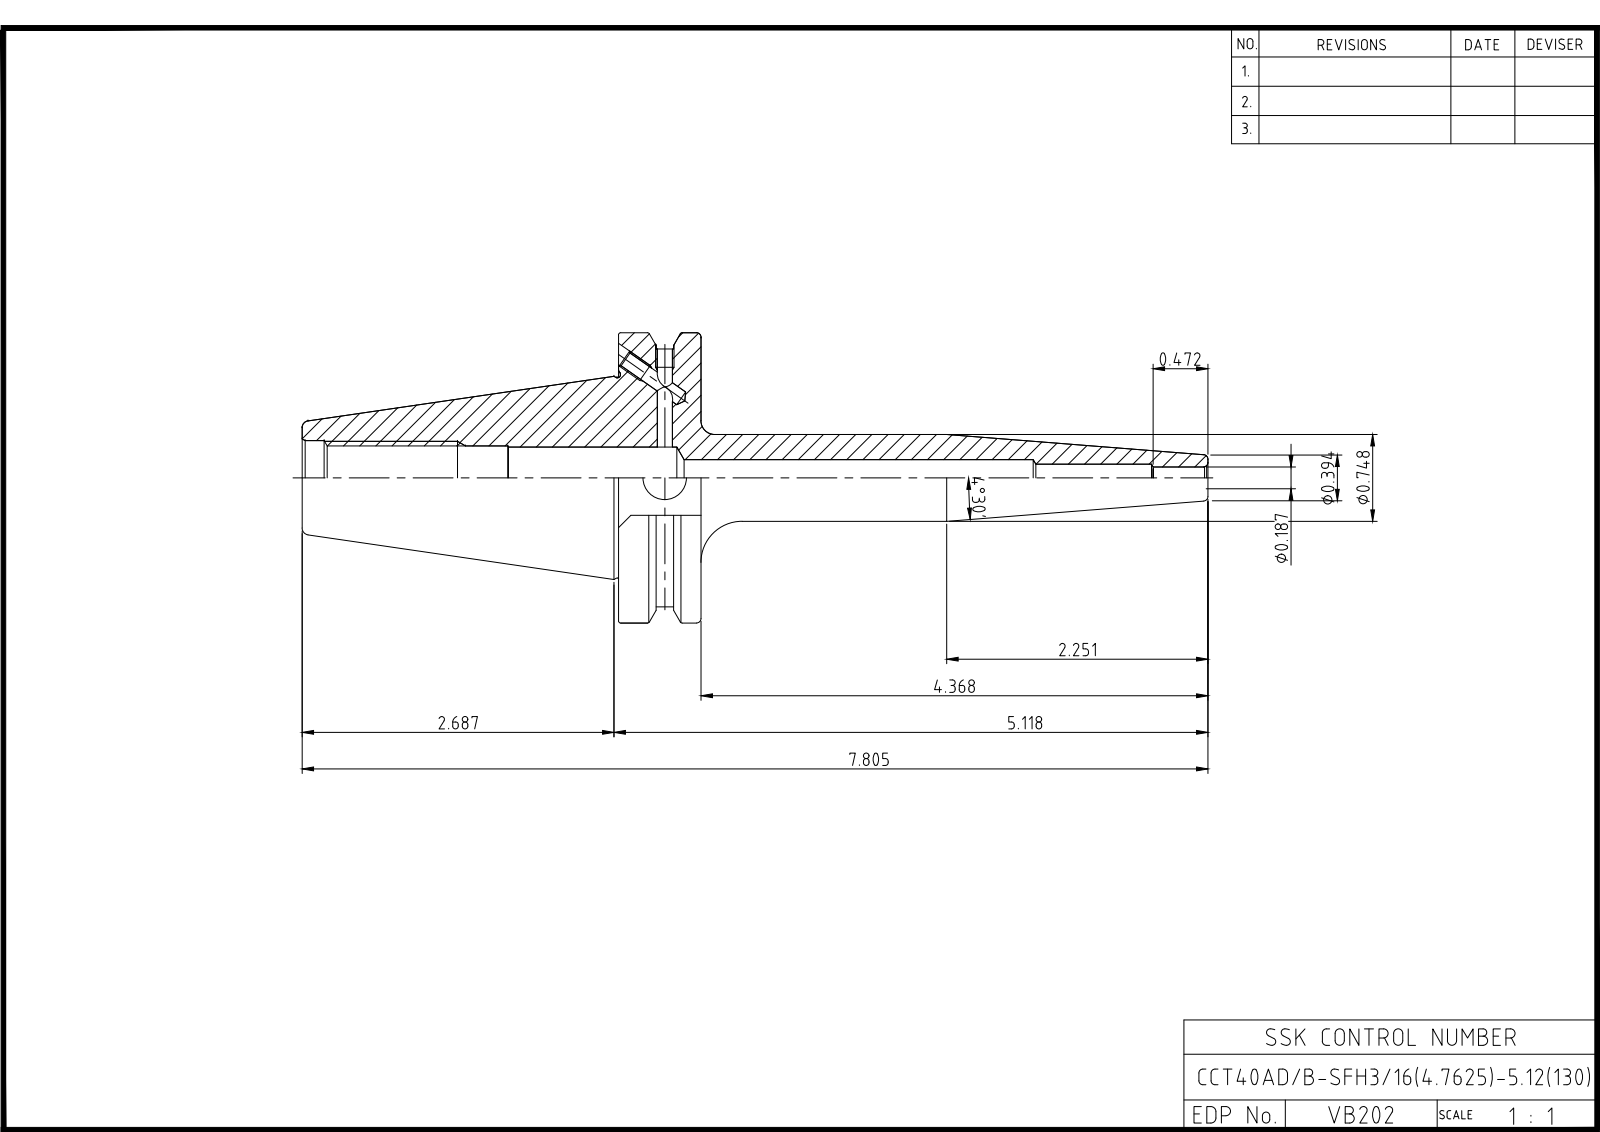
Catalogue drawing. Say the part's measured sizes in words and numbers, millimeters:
The part is named "LO CCT40ADB-SFH4.7625-5.12". Its 3-D file was written by "Autodesk Inventor 2022 (AUTOMOTIVE_DESIGN)". It is 1 solid with 90 faces: 36 planar, 29 cylindrical and 25 other. Overall it measures 198.25 by 63.5 by 61.09 millimeters. Its volume is 125 193 cubic millimeters and its surface area 29 195 square millimeters. Round holes: 4 of diameter 3.24, 2 of diameter 4, 2 of diameter 4.2, 1 of diameter 4.76, 1 of diameter 6, 1 of diameter 8, 1 of diameter 9.53, 1 of diameter 13, 1 of diameter 13.39, 1 of diameter 16.3. Round bosses or shafts: 1 of diameter 63.5, 1 of diameter 43.8, 1 of diameter 19. Partial cylindrical surfaces (rounded edges, fillets, slot ends): 1 of radius 28.15. The main face-to-face distances are 18.05, 47.6, 16.38, 69.25, 87.3, 81.34, 12.09, 5.96, 77.51, 8.26.
